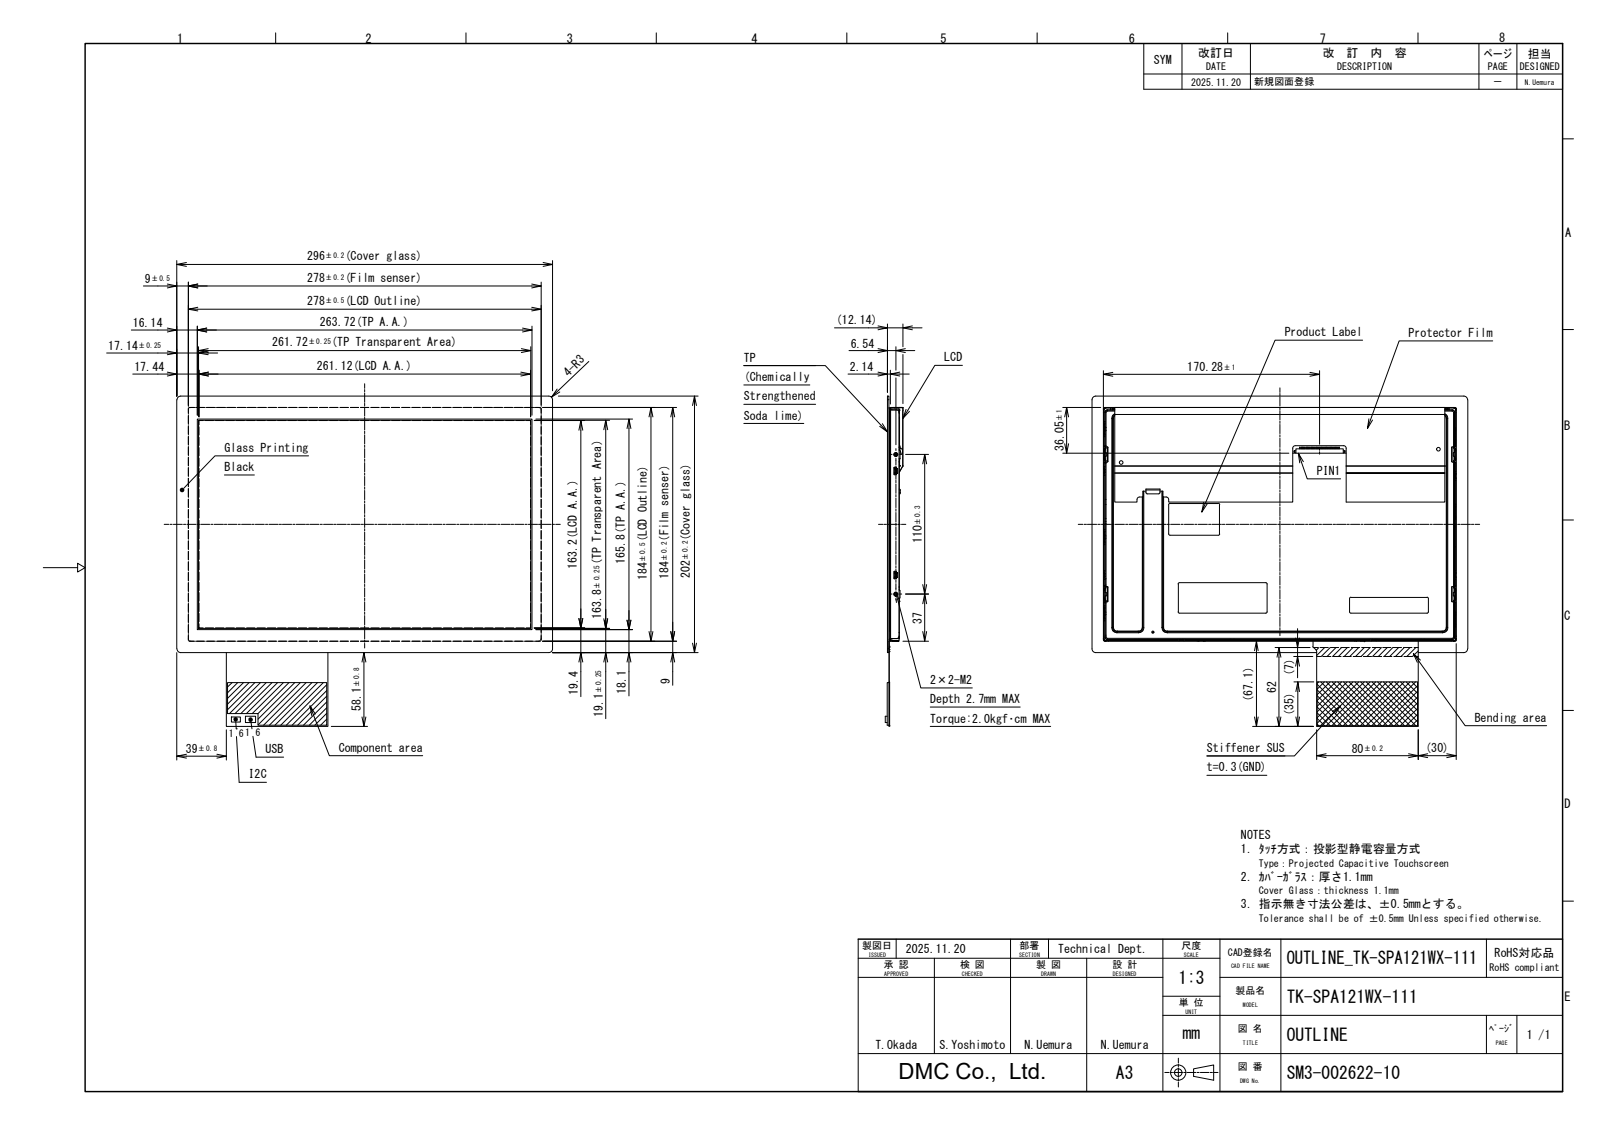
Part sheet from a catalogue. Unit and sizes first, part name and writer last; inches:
Units: inches
Overall size (bounding box): 11.654 × 10.24 × 0.547
Round holes (diameter × count): ⌀0.039 ×4, ⌀0.079 ×4, ⌀0.071 ×3, ⌀0.118 ×2, ⌀0.126 ×2, ⌀0.198 ×2
Round bosses / shafts (diameter × count): ⌀0.157 ×4, ⌀0.118 ×2, ⌀0.083 ×1
Partial cylindrical surfaces — rounded edges, fillets, slot ends (radius × count): R0.02 ×192, R0.039 ×159, R0.008 ×143, R0.012 ×135, R0.004 ×95, R0.016 ×39, R0.035 ×36, R0.031 ×33
Main face-to-face distances: 0.031, 0.113, 0.192, 0.305, 0.224, 0.337, 0.135, 0.035, 0.293, 0.043
Hole centre spacings: 7.091, 10.791, 12.912, 0.157, 0.431, 0.451, 0.478, 0.921
Volume: 13.51 in³ · Surface area: 517 in²
Bodies: 1 solid, 4407 faces (2987 planar, 1097 cylindrical, 323 other)
Part name (STEP PRODUCT): TK-SPA121WX-111
STEP written by: Autodesk Inventor 2024 (AUTOMOTIVE_DESIGN)
